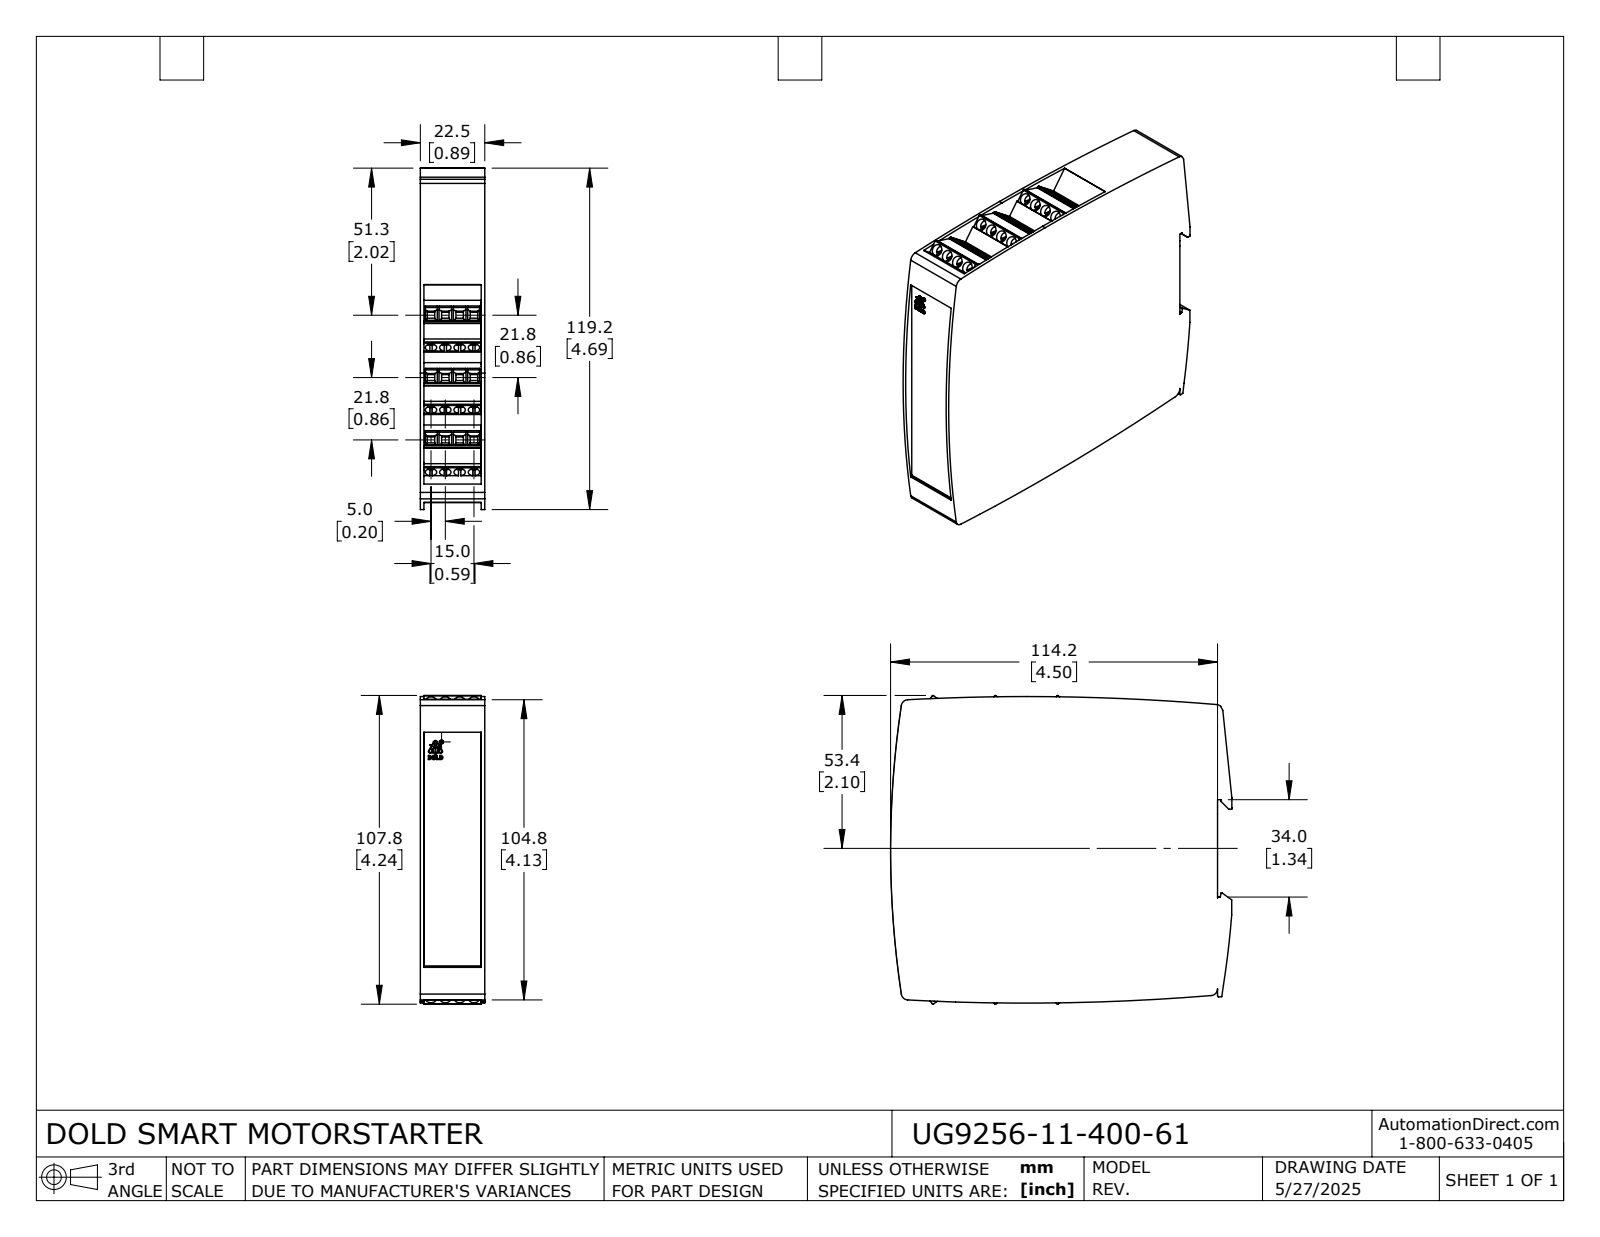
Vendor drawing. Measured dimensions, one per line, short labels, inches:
name: UG9256-11-400-61
written by: SolidWorks 2024 (AUTOMOTIVE_DESIGN)
unit: in
bodies: 1 solid, 1036 faces (813 planar, 222 cylindrical, 1 other)
size: 4.693 × 4.243 × 0.886
volume: 15.85 in³; area: 64.72 in²
holes: 24× ⌀0.157, 1× ⌀0.053
bosses: 24× ⌀0.15, 1× ⌀0.049
rounds: 15× R0.012, 14× R0.02, 12× R0.004, 7× R0.094, 6× R0.005, 4× R0.004, 4× R31.496, 3× R0.021
face distances: 0.886, 0.049, 0.837, 0.675, 4.379, 0.051, 0.835, 1.35, 0.528, 0.785
hole spacings: 0.563, 0.197, 0.528, 0.658, 0.394, 1.073, 0.792, 1.055
